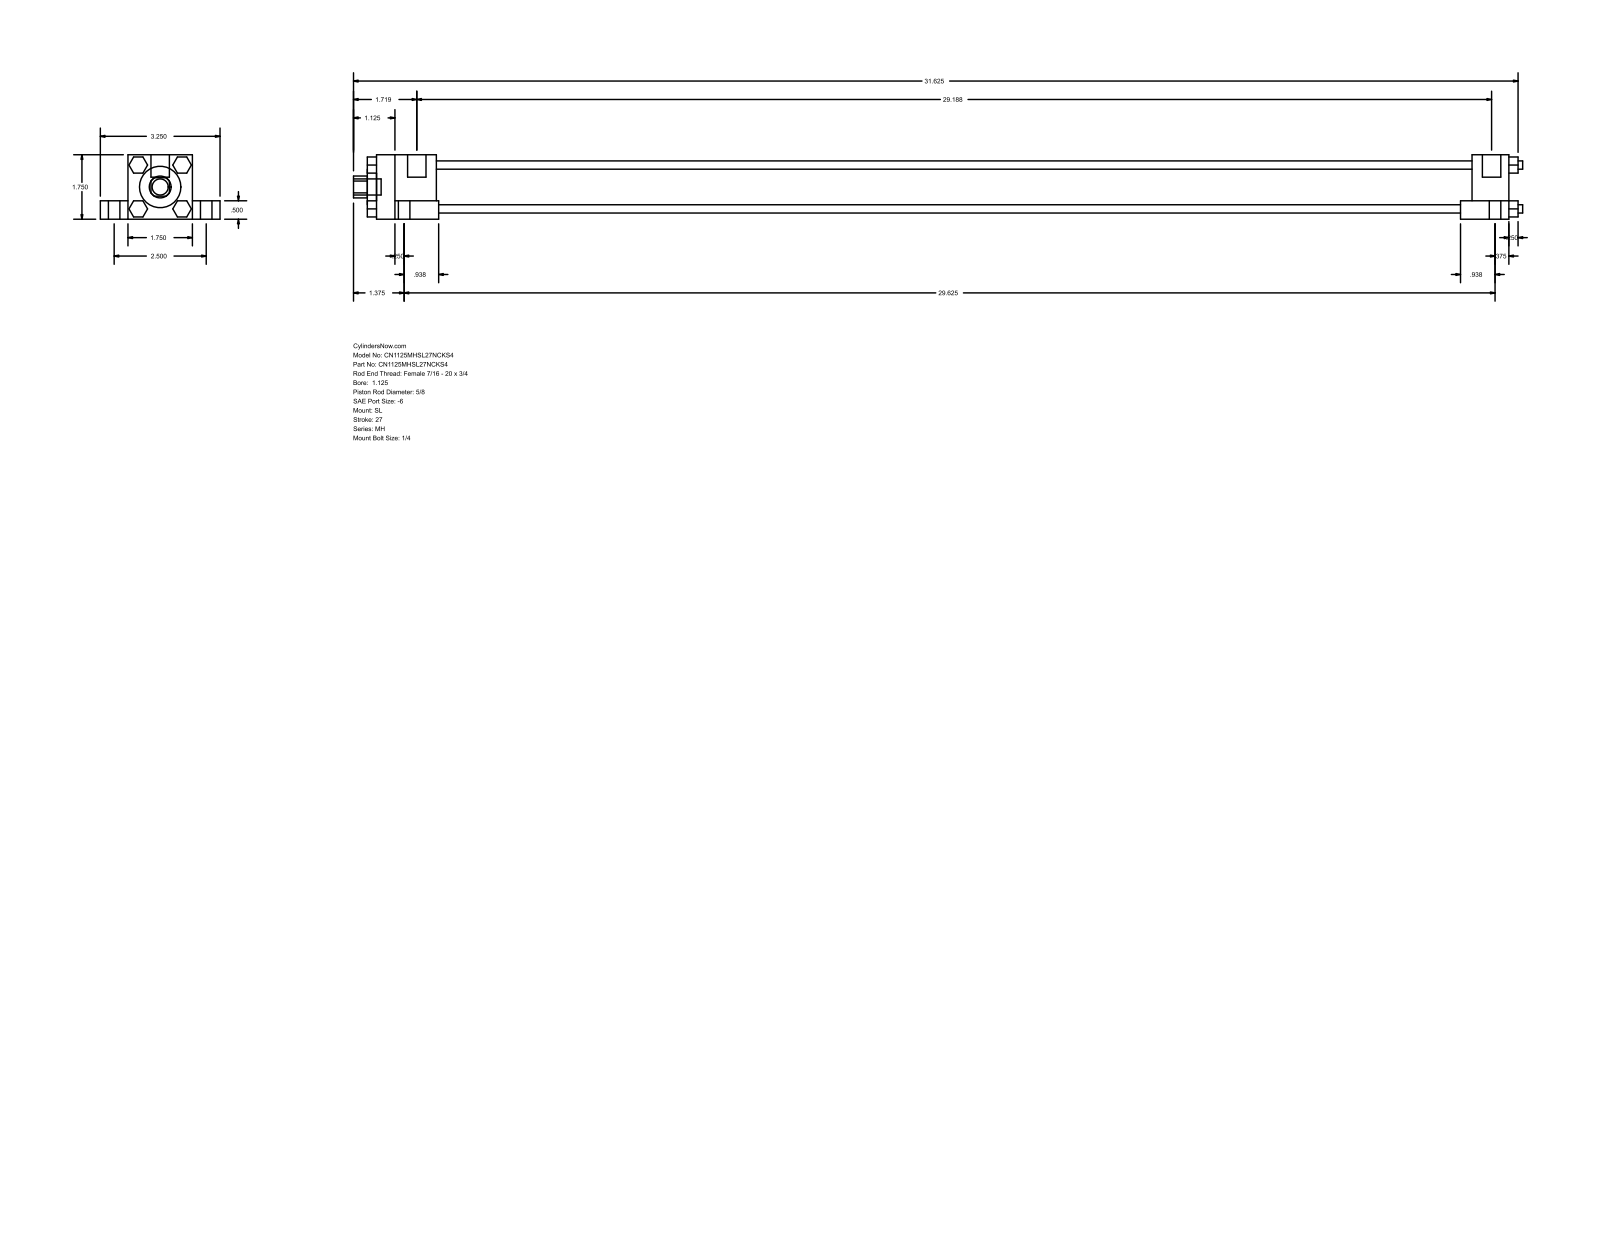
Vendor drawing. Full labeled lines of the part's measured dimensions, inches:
Part name (STEP PRODUCT): MH_SL__0112_0.625
STEP written by: GSSL Pune (CONFIG_CONTROL_DESIGN)
Units: inches
Bodies: 0 solids, 150 faces (114 planar, 36 cylindrical, 0 other)
Overall size (bounding box): 31.75 × 3.25 × 1.75
Round holes (diameter × count): ⌀0.625 ×1, ⌀1.125 ×1, ⌀1.375 ×1
Round bosses / shafts (diameter × count): ⌀0.563 ×4, ⌀0.313 ×4, ⌀0.225 ×4, ⌀0.219 ×4, ⌀0.5 ×2, ⌀0.437 ×1
Partial cylindrical surfaces — rounded edges, fillets, slot ends (radius × count): R0.297 ×1
Main face-to-face distances: 1.75, 0.75, 0.5, 1.25, 2.5, 0.25, 31, 0.437, 28.125, 29.125
